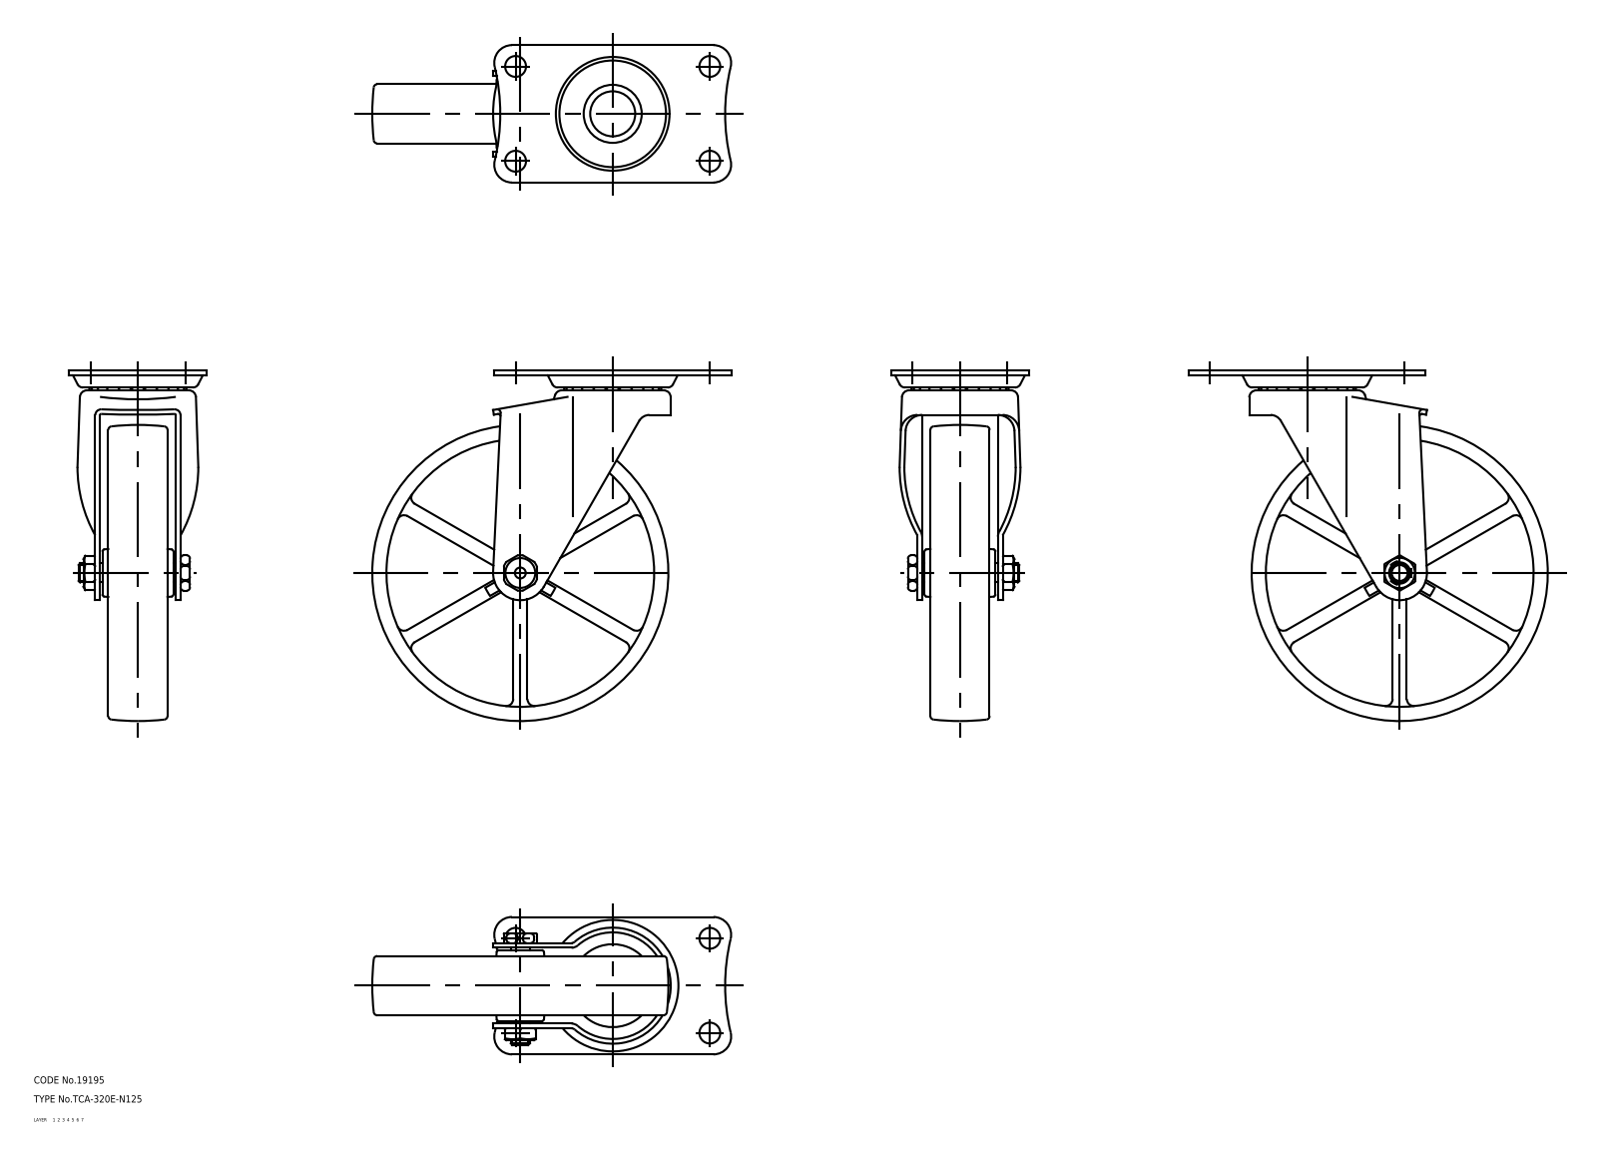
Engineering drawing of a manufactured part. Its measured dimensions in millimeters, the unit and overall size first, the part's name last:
Units: millimetres
Overall size (bounding box): 151.5 × 148 × 58
Volume: 261 059 mm³ · Surface area: 79 705 mm²
Bodies: 5 solids, 596 faces (0 planar, 0 cylindrical, 596 other)
Part name (STEP PRODUCT): wheel; mounting plate; main shaft; axle (+1 more)
STEP written by: CADfix (AUTOMOTIVE_DESIGN)
